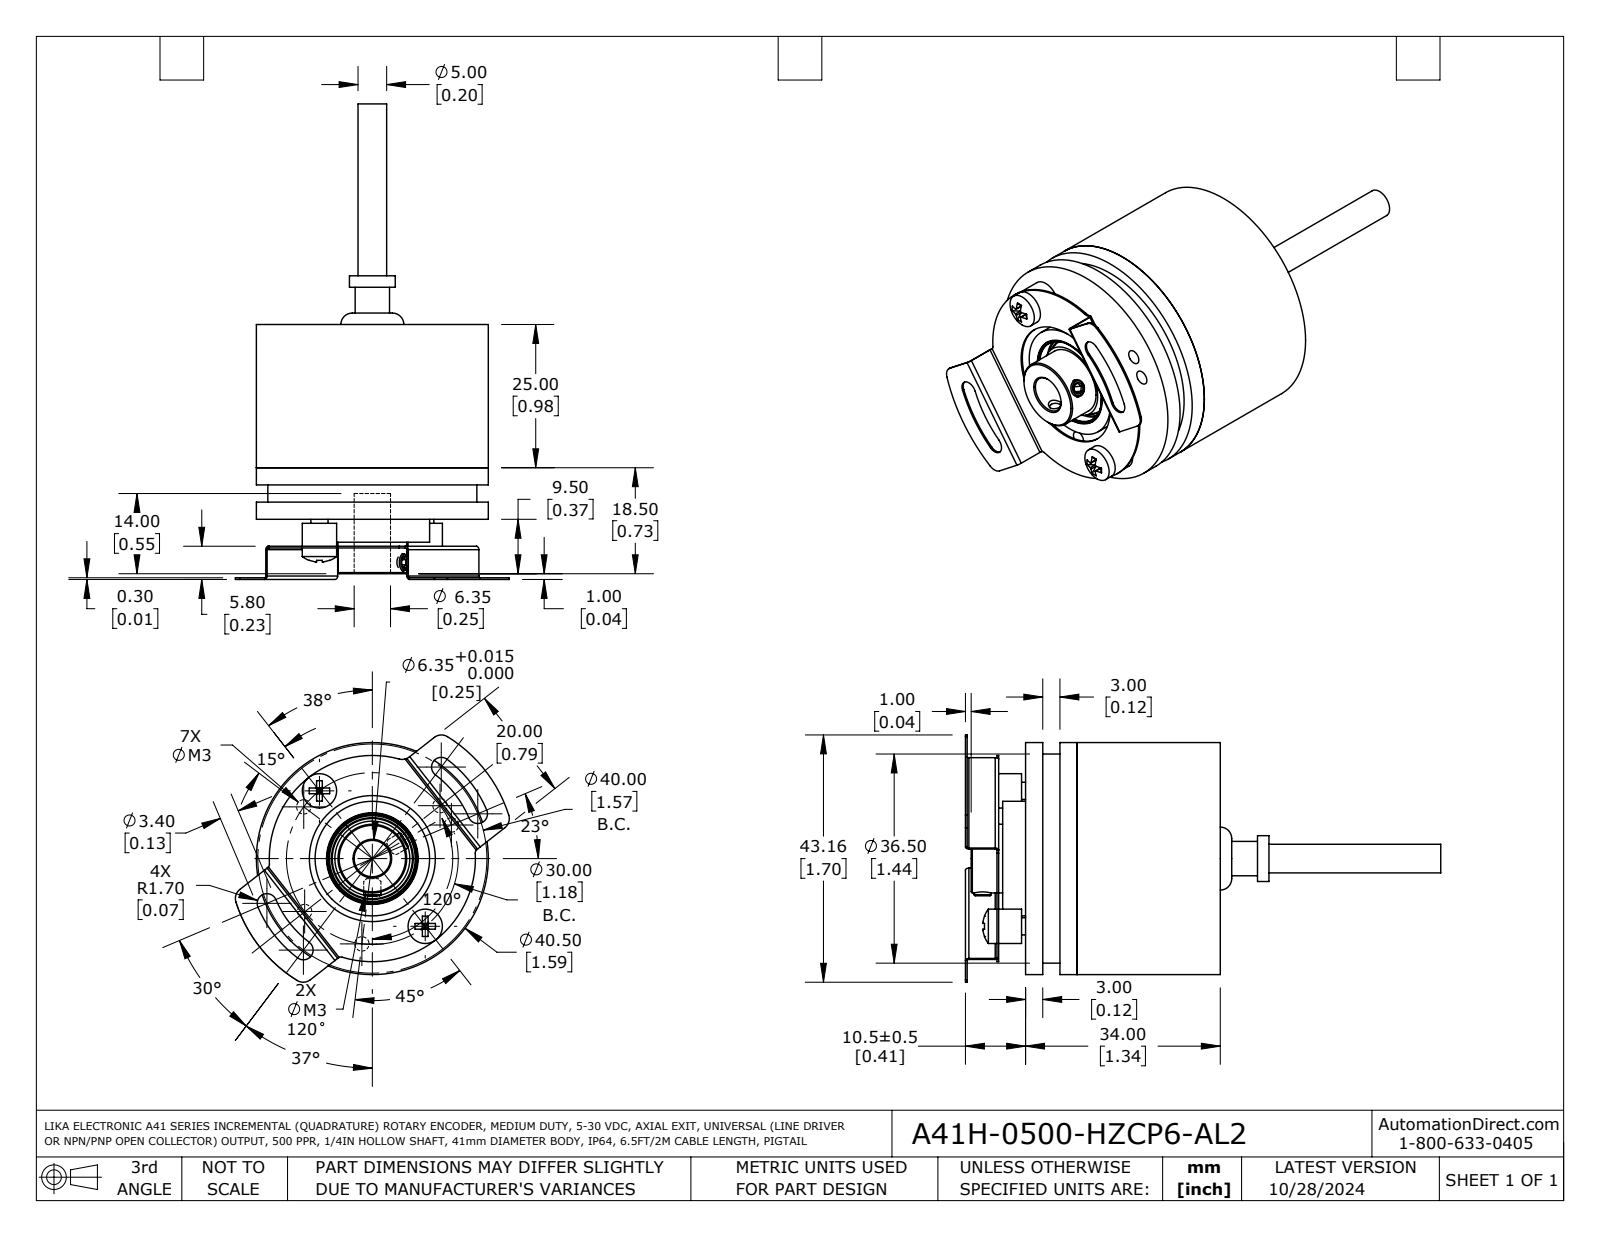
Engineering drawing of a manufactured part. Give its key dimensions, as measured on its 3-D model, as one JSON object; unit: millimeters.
{"part_name": "A41H-0500-HZCP6-AL2", "step_written_by": "SolidWorks 2021 (AUTOMOTIVE_DESIGN)", "units": "millimeters", "bodies": {"solids": 15, "faces": 465, "planar": 139, "cylindrical": 186, "other": 140}, "overall_size": [83, 47.8, 43.2], "volume_mm3": 19450, "surface_area_mm2": 20890, "round_holes": [[2.5, 9], [1.6, 7], [4, 3], [2.2, 2], [3.2, 2], [3.5, 2], [4.3, 1], [6.4, 1], [7.5, 1], [13, 1], [15.3, 1], [15.5, 1]], "round_bosses_or_shafts": [[3, 4], [6, 3], [3.8, 2], [2, 2], [40.5, 1], [38, 1], [37, 1], [36.5, 1]], "partial_cylinders_radius": [[1, 14], [0.2, 8], [2, 5], [0.3, 4], [0.6, 4], [1.7, 4], [0.8, 3], [18, 1]], "face_to_face_distances": [3, 11, 34, 23, 5, 31, 2, 22, 1, 20], "hole_center_spacings": [15, 17, 21.2, 2.8, 3, 21.3, 24, 26]}
